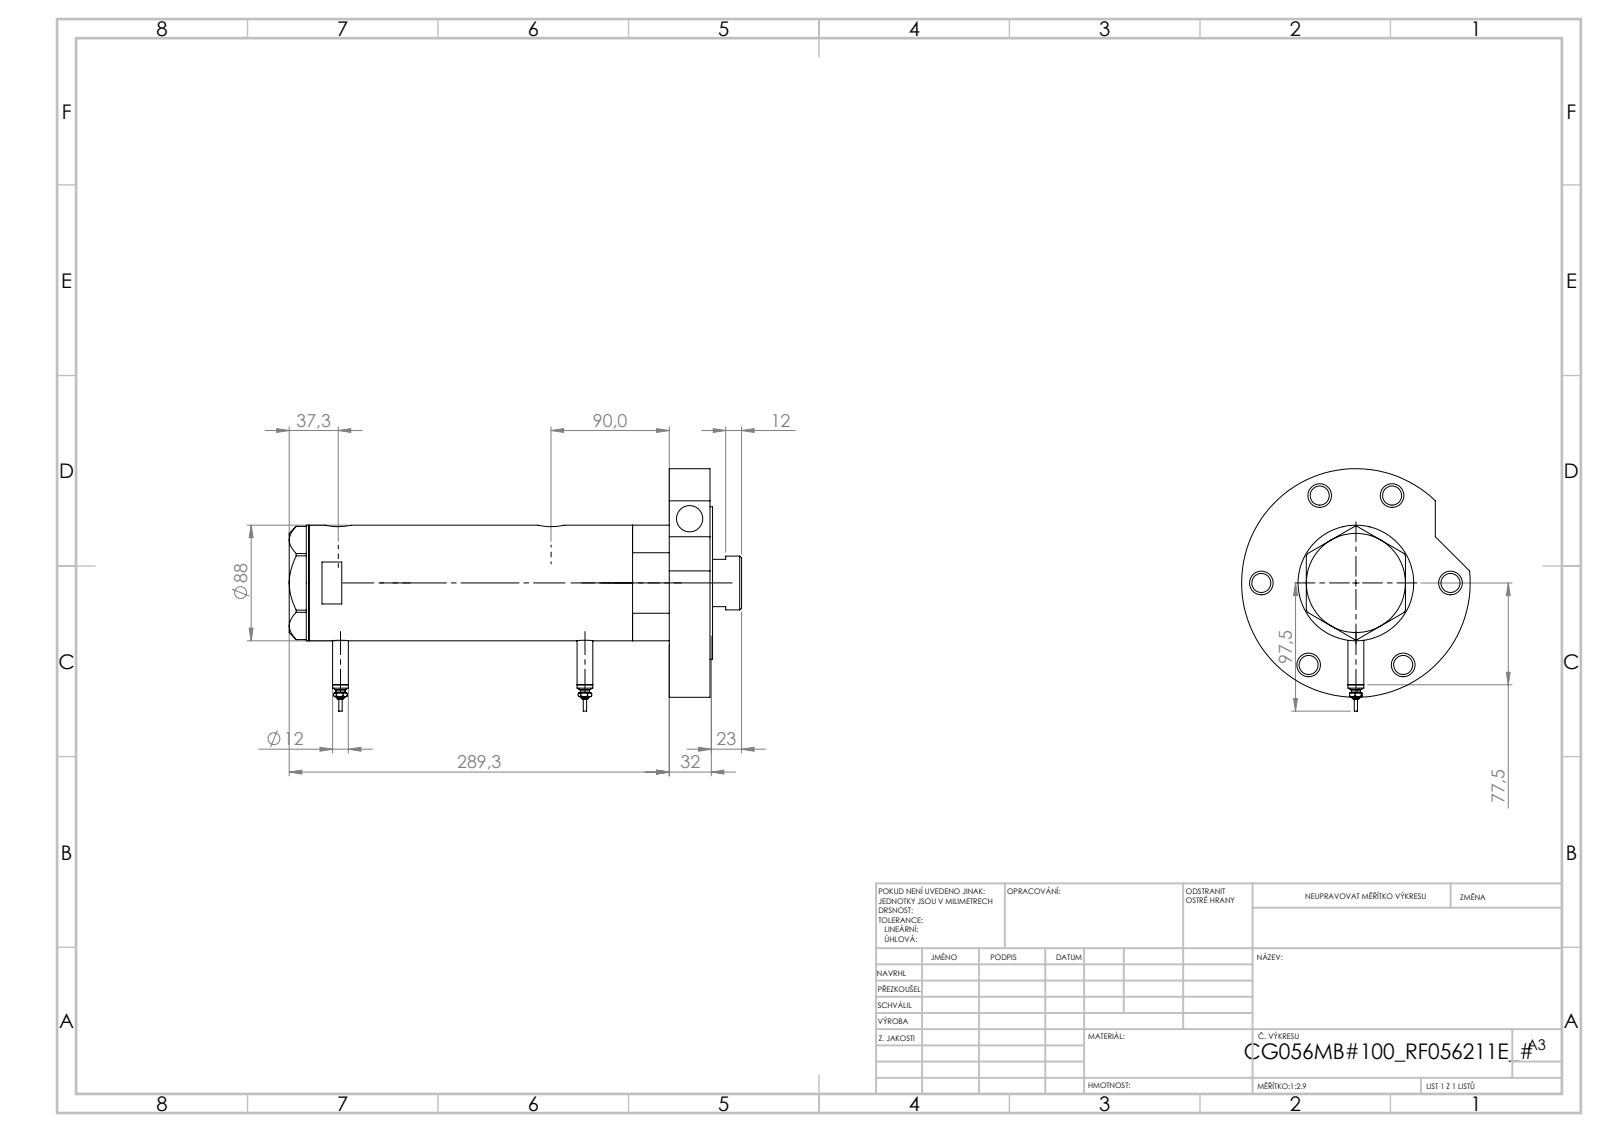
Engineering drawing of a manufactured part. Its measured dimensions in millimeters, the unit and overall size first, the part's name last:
Units: millimetres
Overall size (bounding box): 344.3 × 184.5 × 174
Round holes (diameter × count): ⌀14.5 ×7, ⌀18 ×6, ⌀20 ×3, ⌀12.5 ×2, ⌀13.16 ×2, ⌀42 ×1, ⌀43.5 ×1, ⌀56 ×1, ⌀60 ×1, ⌀75 ×1, ⌀80 ×1
Round bosses / shafts (diameter × count): ⌀12 ×2, ⌀9 ×2, ⌀7 ×2, ⌀4.5 ×2, ⌀2.5 ×2, ⌀174 ×1, ⌀116 ×1, ⌀88 ×1
Main face-to-face distances: 31, 2, 307.3, 274.3, 305.3, 33, 184.4, 89.9, 120.9, 122.9
Hole centre spacings: 72, 80, 119.73, 124.71, 129.15, 143.69, 1.7, 25.8
Volume: 2 311 000 mm³ · Surface area: 331 475 mm²
Bodies: 7 solids, 257 faces (91 planar, 102 cylindrical, 64 other)
Part name (STEP PRODUCT): V270CG_FRONT; V270CG_MIDDLE; V270CG_RF211E; V270CG_BACK (+2 more)
STEP written by: SolidWorks 2019 (CONFIG_CONTROL_DESIGN)
